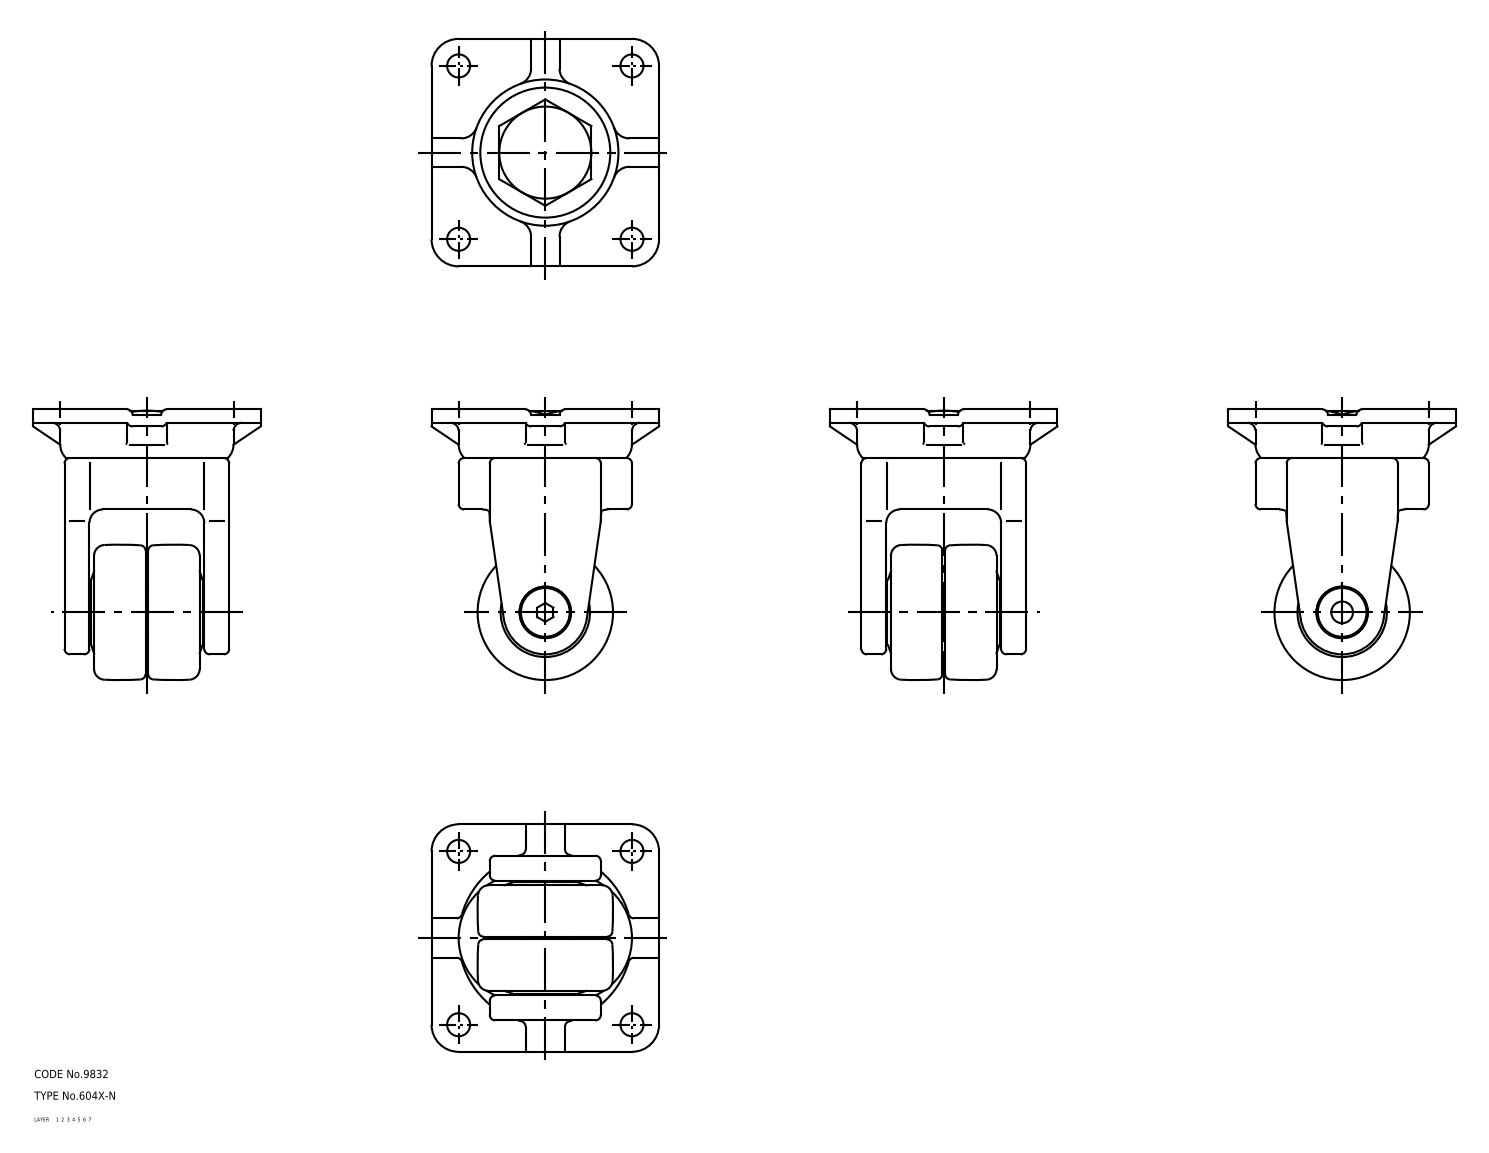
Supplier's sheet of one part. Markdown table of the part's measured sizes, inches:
| quantity | value |
| --- | --- |
| part name | 67137331; 67137344; 67137357; 67137370 (+1 more) |
| STEP written by | CADfix (AUTOMOTIVE_DESIGN) |
| units | inches |
| bodies | 5 solids, 392 faces (0 planar, 0 cylindrical, 392 other) |
| overall size | 3.937 × 3.307 × 3.307 |
| volume | 12.94 in³ |
| surface area | 94.22 in² |
